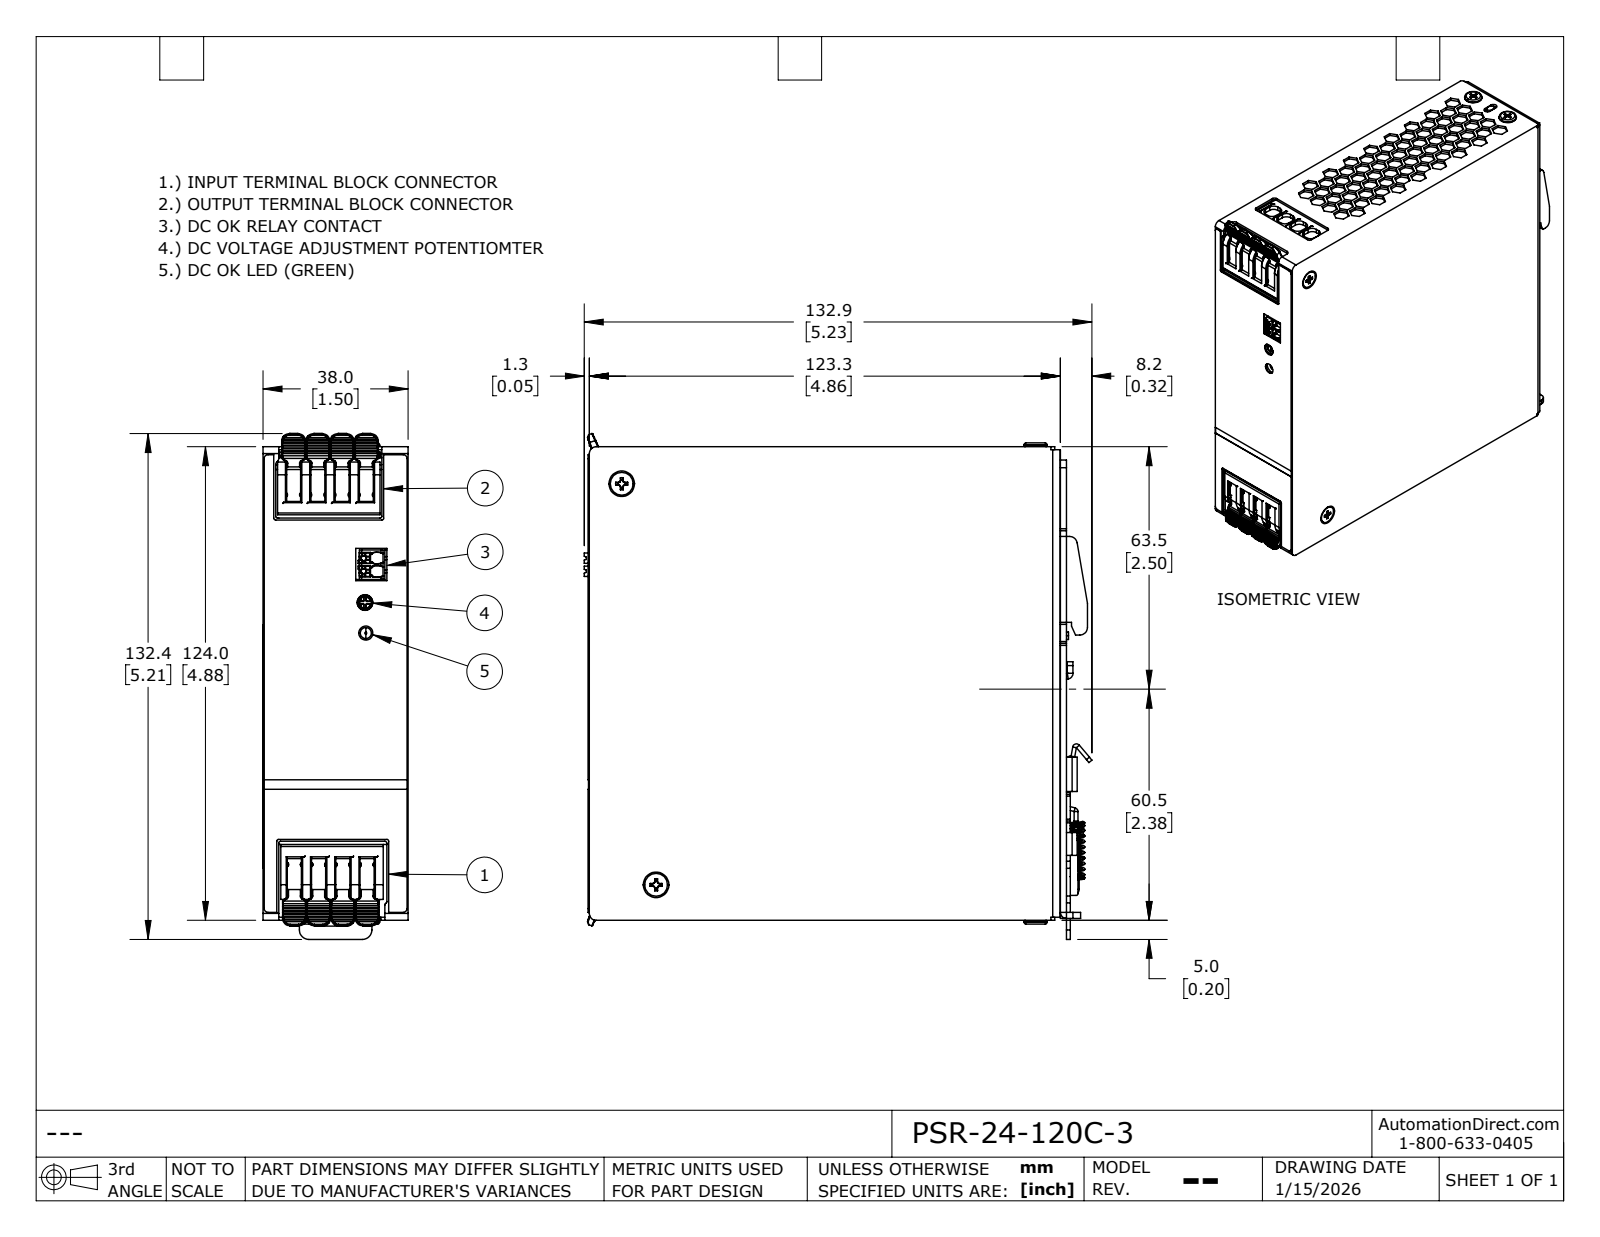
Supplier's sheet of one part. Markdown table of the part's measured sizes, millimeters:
| quantity | value |
| --- | --- |
| part name | PSR-24-120C-3 |
| STEP written by | SolidWorks 2024 (AUTOMOTIVE_DESIGN) |
| units | millimeters |
| bodies | 3 solids, 3798 faces (2633 planar, 779 cylindrical, 386 other) |
| overall size | 132.94 × 132.45 × 38.08 |
| volume | 578 989 mm³ |
| surface area | 63 895 mm² |
| round holes (diameter × count) | 3.9 × 4, 4.5 × 4, 1.3 × 2, 4 × 2, 2 × 1, 3.5 × 1, 3.7 × 1, 4.1 × 1 |
| round bosses / shafts (diameter × count) | 6 × 10, 3 × 2, 3.4 × 1, 2.9 × 1 |
| partial cylindrical surfaces (radius × count) | 0.5 × 100, 0.2 × 99, 2 × 68, 0.3 × 60, 1 × 42, 0.35 × 26, 0.1 × 17, 0.8 × 16 |
| main face-to-face distances | 38, 38.08, 0.8, 123.2, 125.3, 124, 122.4, 1.6, 123.7, 124.19 |
| hole center spacings | 20, 37.85, 65.27, 101, 102.96, 3.4, 7.93, 8 |
